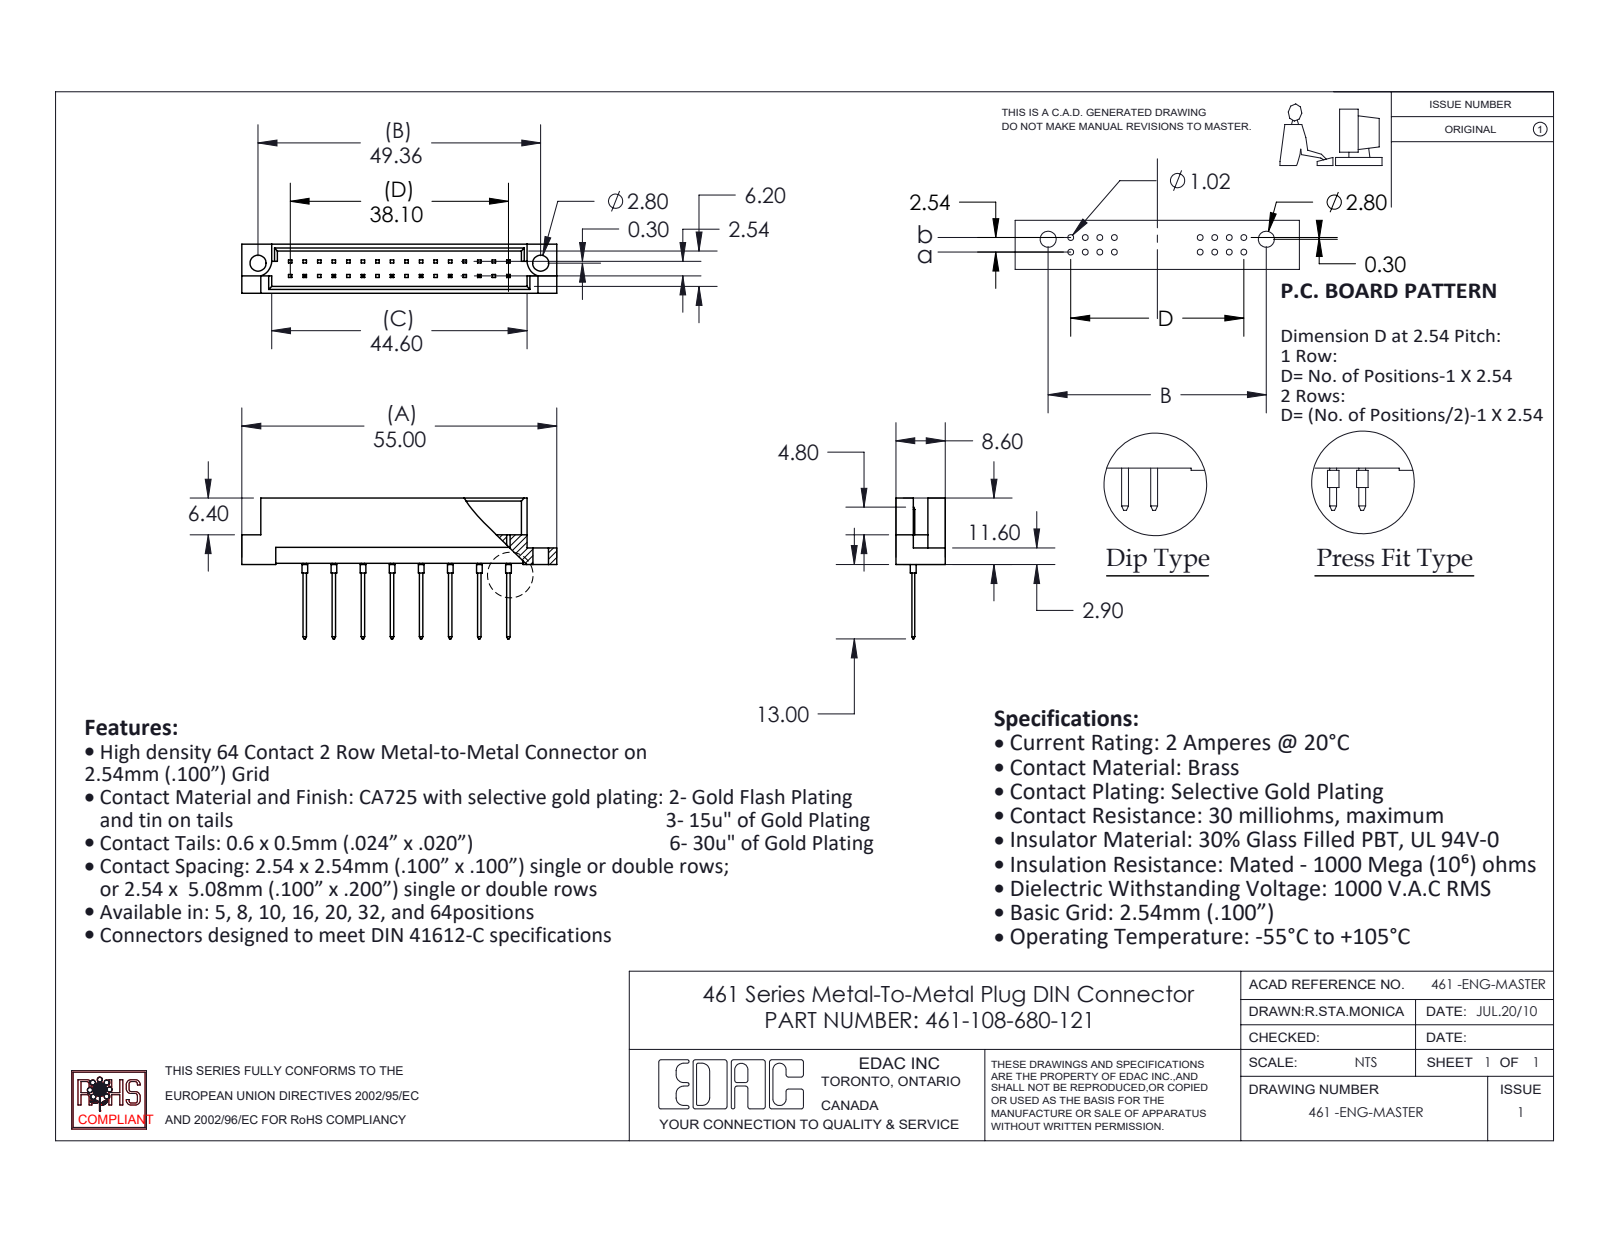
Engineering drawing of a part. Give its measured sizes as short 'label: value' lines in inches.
name: 461-108-680-121; 461 Part_32; 461-290_80
written by: SolidWorks 2020 (CONFIG_CONTROL_DESIGN)
unit: in
bodies: 9 solids, 352 faces (330 planar, 22 cylindrical, 0 other)
size: 2.165 × 0.969 × 0.339
volume: 0.166 in³; area: 5.687 in²
holes: 2× ⌀0.11
bosses: 8× ⌀0.039
rounds: 2× R0.11
face distances: 0.047, 0.291, 0.339, 0.244, 0.197, 0.109, 0.229, 0.062, 0.182, 0.129
hole spacings: 1.943
